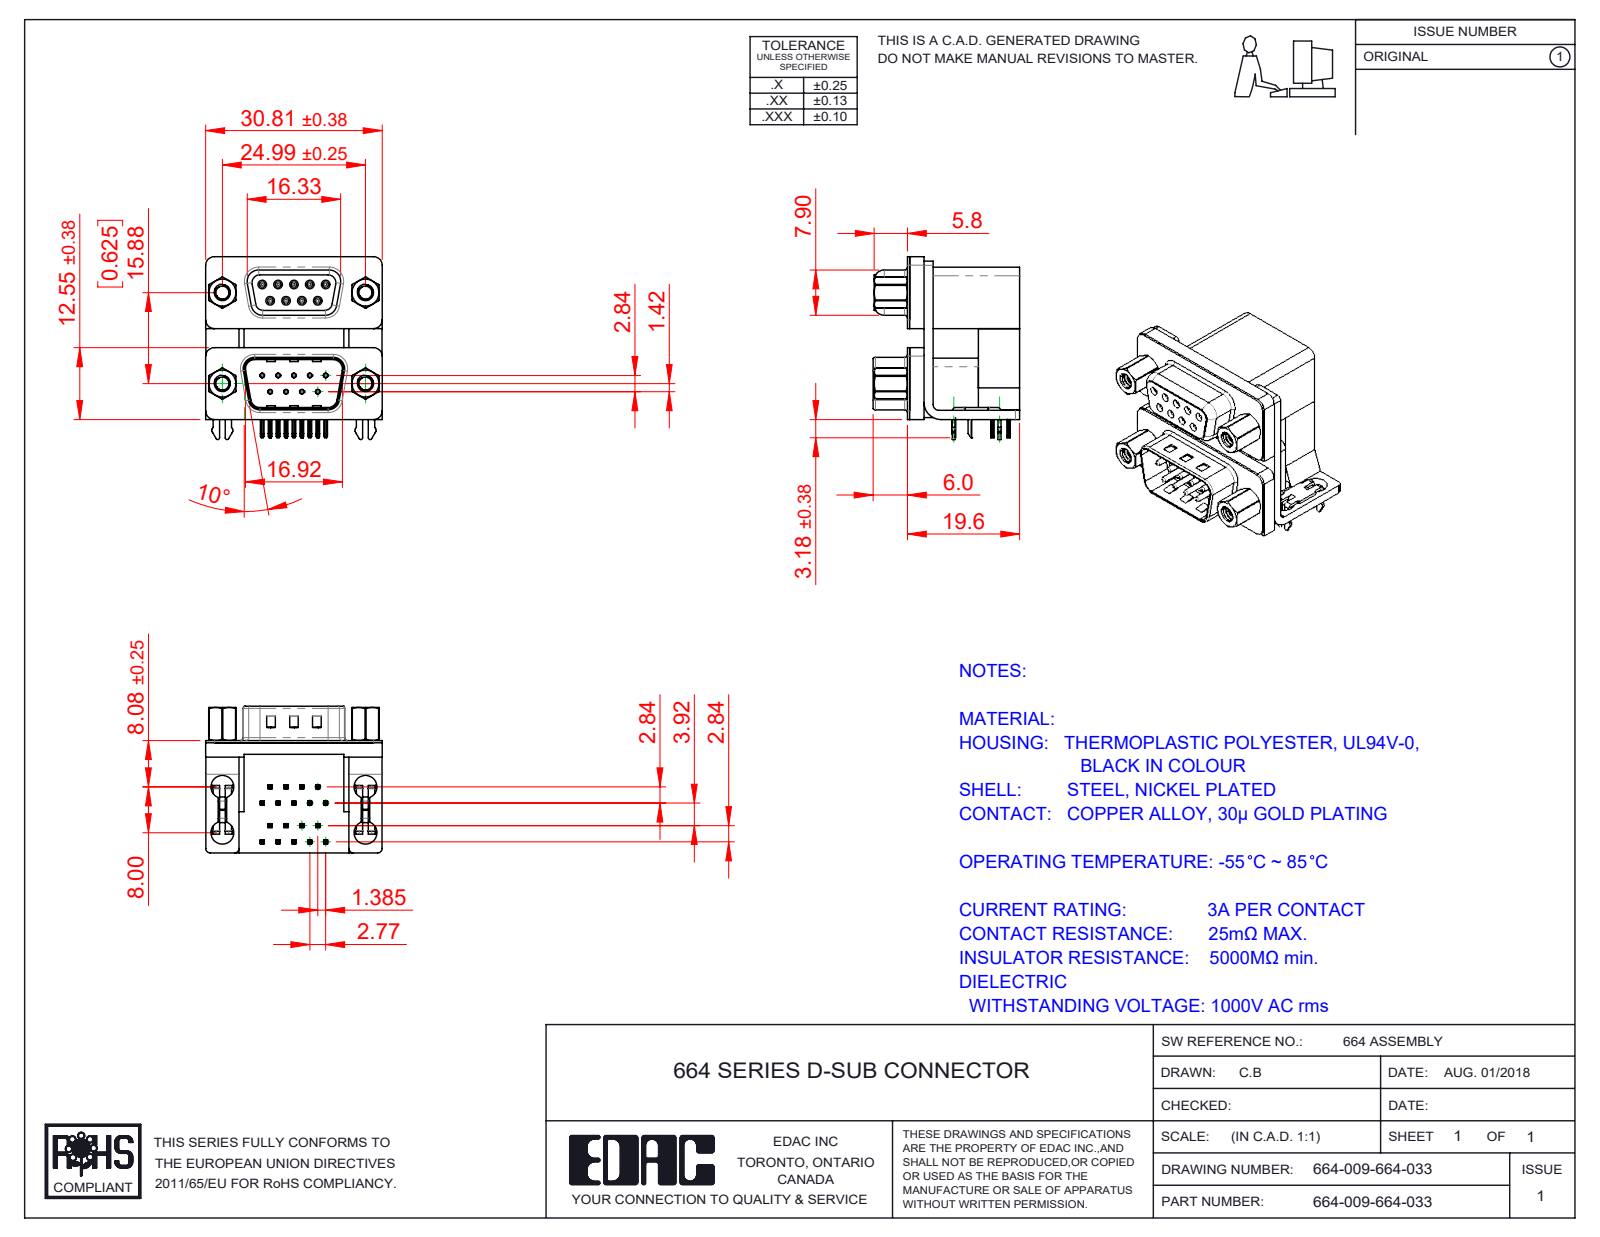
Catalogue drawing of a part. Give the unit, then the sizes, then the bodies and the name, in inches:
Units: inches
Overall size (bounding box): 1.257 × 1.213 × 1.008
Round holes (diameter × count): ⌀0.031 ×18, ⌀0.014 ×9, ⌀0.035 ×9, ⌀0.157 ×8, ⌀0.089 ×4, ⌀0.09 ×4, ⌀0.138 ×4, ⌀0.189 ×4, ⌀0.197 ×4
Round bosses / shafts (diameter × count): ⌀0.047 ×9, ⌀0.03 ×9, ⌀0.193 ×4, ⌀0.187 ×4, ⌀0.154 ×4, ⌀0.11 ×4
Partial cylindrical surfaces — rounded edges, fillets, slot ends (radius × count): R0.004 ×74, R0.01 ×46, R0.006 ×36, R0.005 ×18, R0.014 ×18, R0.02 ×16, R0.059 ×13, R0.03 ×10
Main face-to-face distances: 0.016, 0.098, 0.657, 0.756, 0.772, 0.114, 0.283, 0.374, 0.472, 0.488
Hole centre spacings: 0.124, 0.109, 0.635, 0.625, 0.218, 0.662, 0.984, 0.516
Volume: 0.656 in³ · Surface area: 20.68 in²
Bodies: 35 solids, 2933 faces (1409 planar, 889 cylindrical, 635 other)
Part name (STEP PRODUCT): 664 Mounting Bracket_2ProngL; 664-009-664-033; 664 4-40 Hex Standoff 5; 664 Contact Bottom Lower (+8 more)
STEP written by: SolidWorks 2020 (CONFIG_CONTROL_DESIGN)
